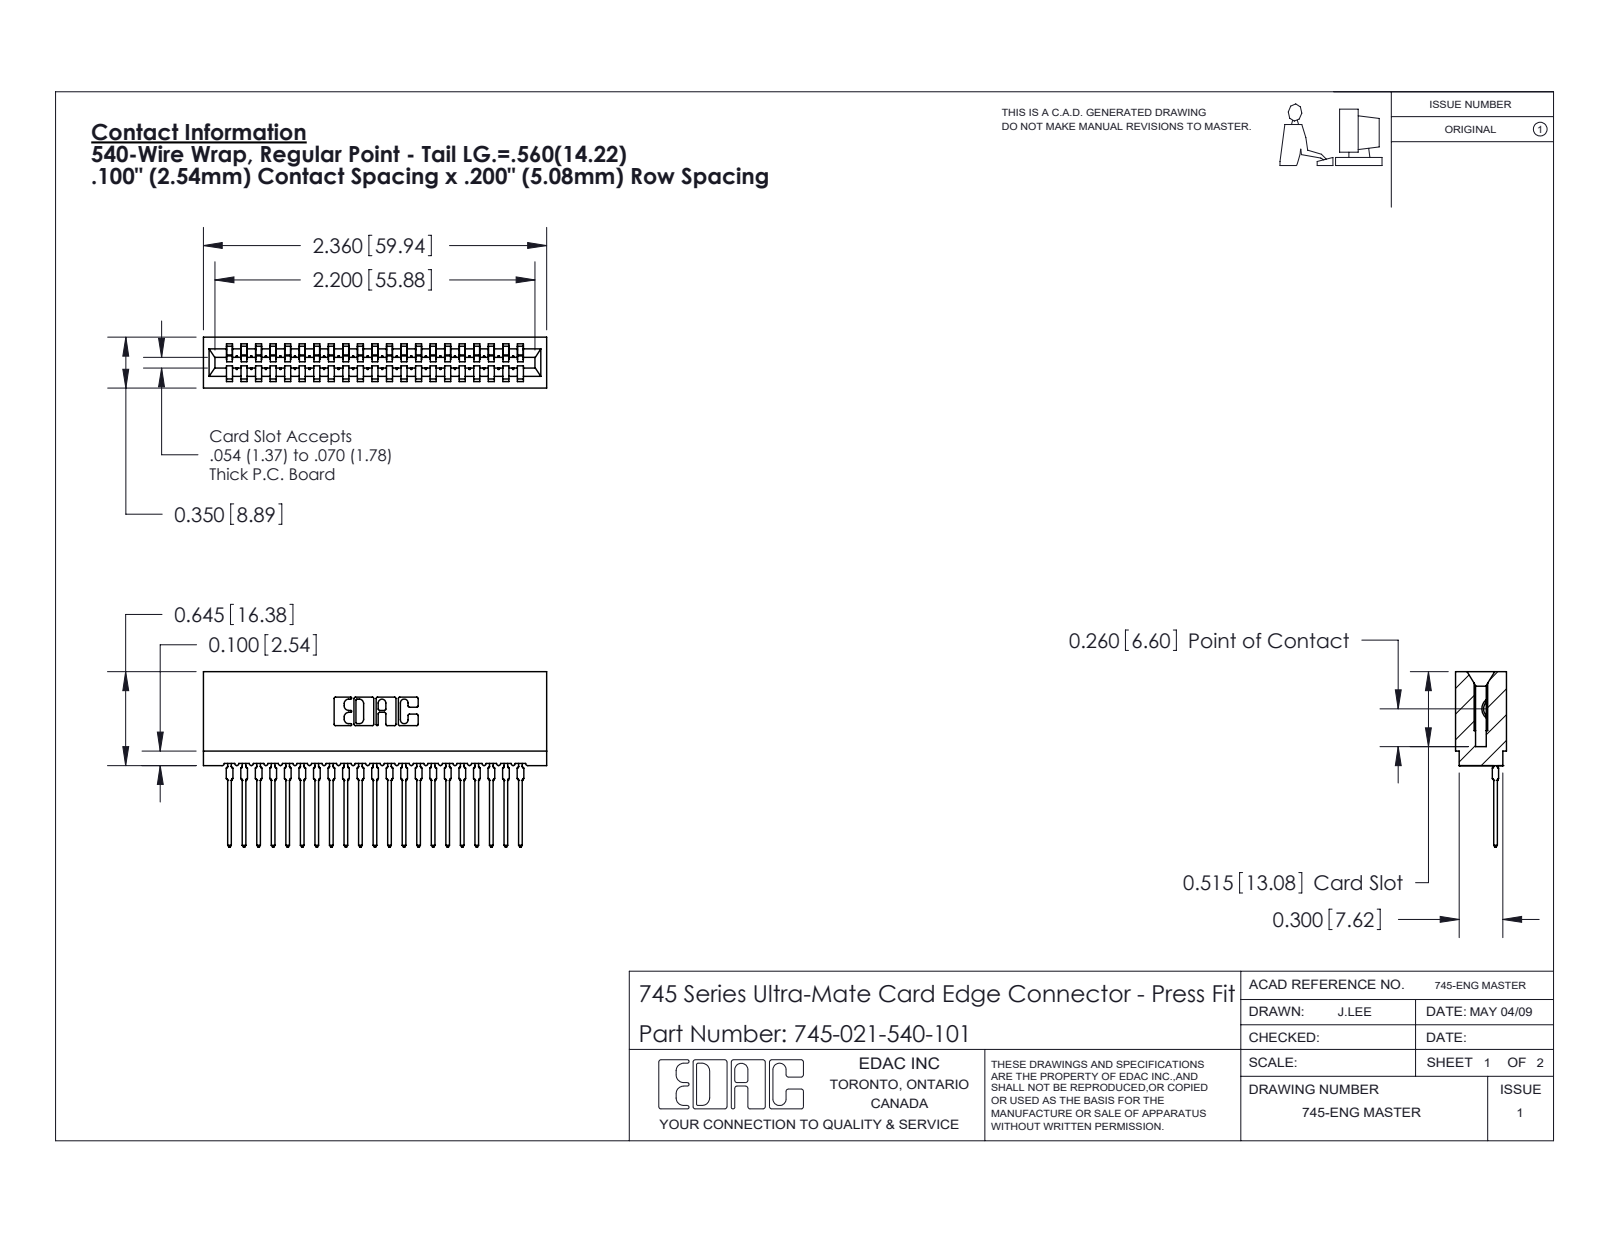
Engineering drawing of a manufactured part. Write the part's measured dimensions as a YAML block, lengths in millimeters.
part_name: "745-021-540-101; 745-292-001_540; 745 Part_Insulator Option - 01"
step_written_by: "SolidWorks 2020 (CONFIG_CONTROL_DESIGN)"
units: millimeters
bodies: {solids: 22, faces: 2447, planar: 1462, cylindrical: 439, other: 546}
overall_size: [59.9, 30.6, 8.9]
volume: 5370
surface_area: 9845
partial_cylinders:
  - {radius: 0.4, count: 42}
  - {radius: 0.5, count: 42}
  - {radius: 0.3, count: 22}
  - {radius: 0.2, count: 6}
  - {radius: 0.8, count: 6}
  - {radius: 0.1, count: 4}
  - {radius: 0.3, count: 4}
  - {radius: 0.7, count: 3}
face_to_face_distances: [2.5, 5.1, 8.9, 7.6, 12.7, 10.2, 3.5, 5.4, 1.1, 7.7]
